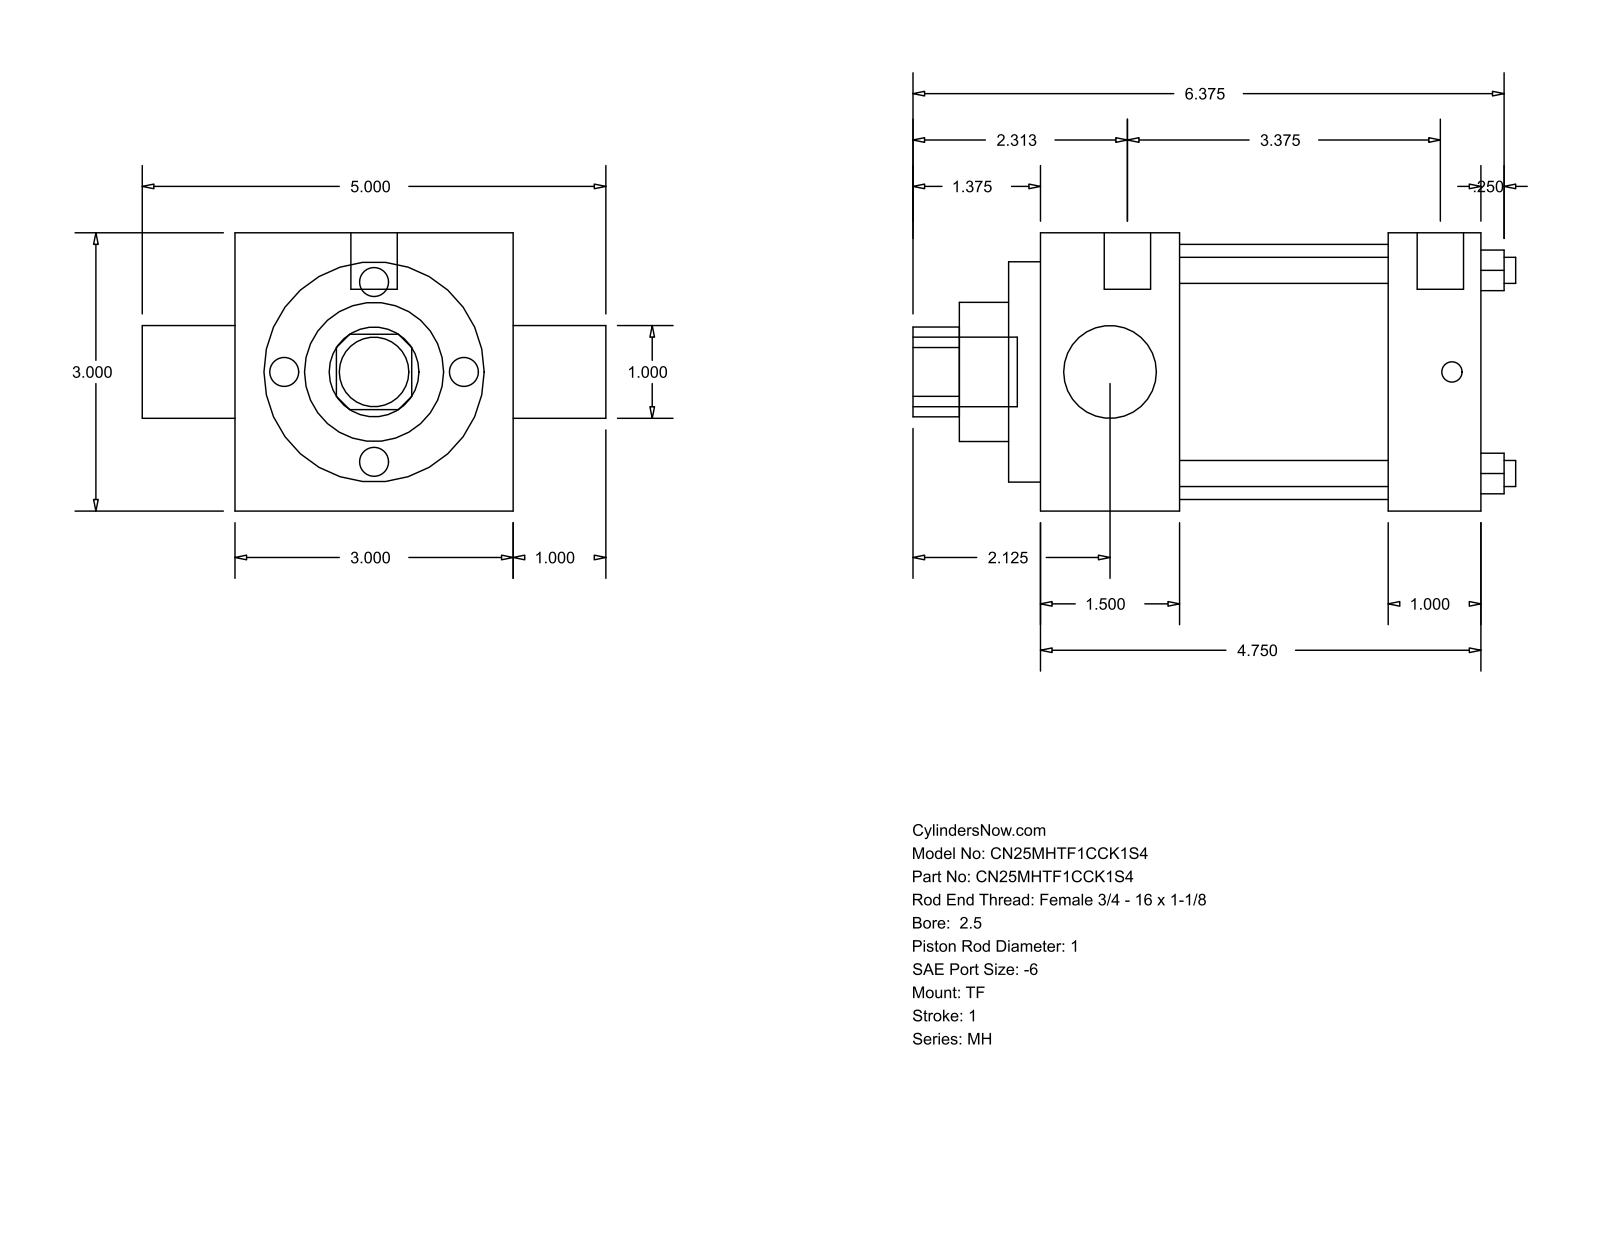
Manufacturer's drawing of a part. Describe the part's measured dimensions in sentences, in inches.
The part is named "MH_TF__0250_1". Its 3-D file was written by "GSSL Pune (CONFIG_CONTROL_DESIGN)". It is 0 solids with 86 faces: 61 planar, 25 cylindrical and 0 other. Overall it measures 6.5 by 5 by 3 inches. Round holes: 4 of diameter 0.281, 2 of diameter 1, 1 of diameter 1.5, 1 of diameter 2.375, 1 of diameter 2.75. Round bosses or shafts: 3 of diameter 0.219, 2 of diameter 0.5, 1 of diameter 0.75. Partial cylindrical surfaces (rounded edges, fillets, slot ends): 1 of radius 0.484. The main face-to-face distances are 3, 4.75, 1, 1.5, 3.25, 3.75, 2.25, 0.344, 1.844, 4.094. The hole center spacings are 1.548, 2.19, 3.097.
